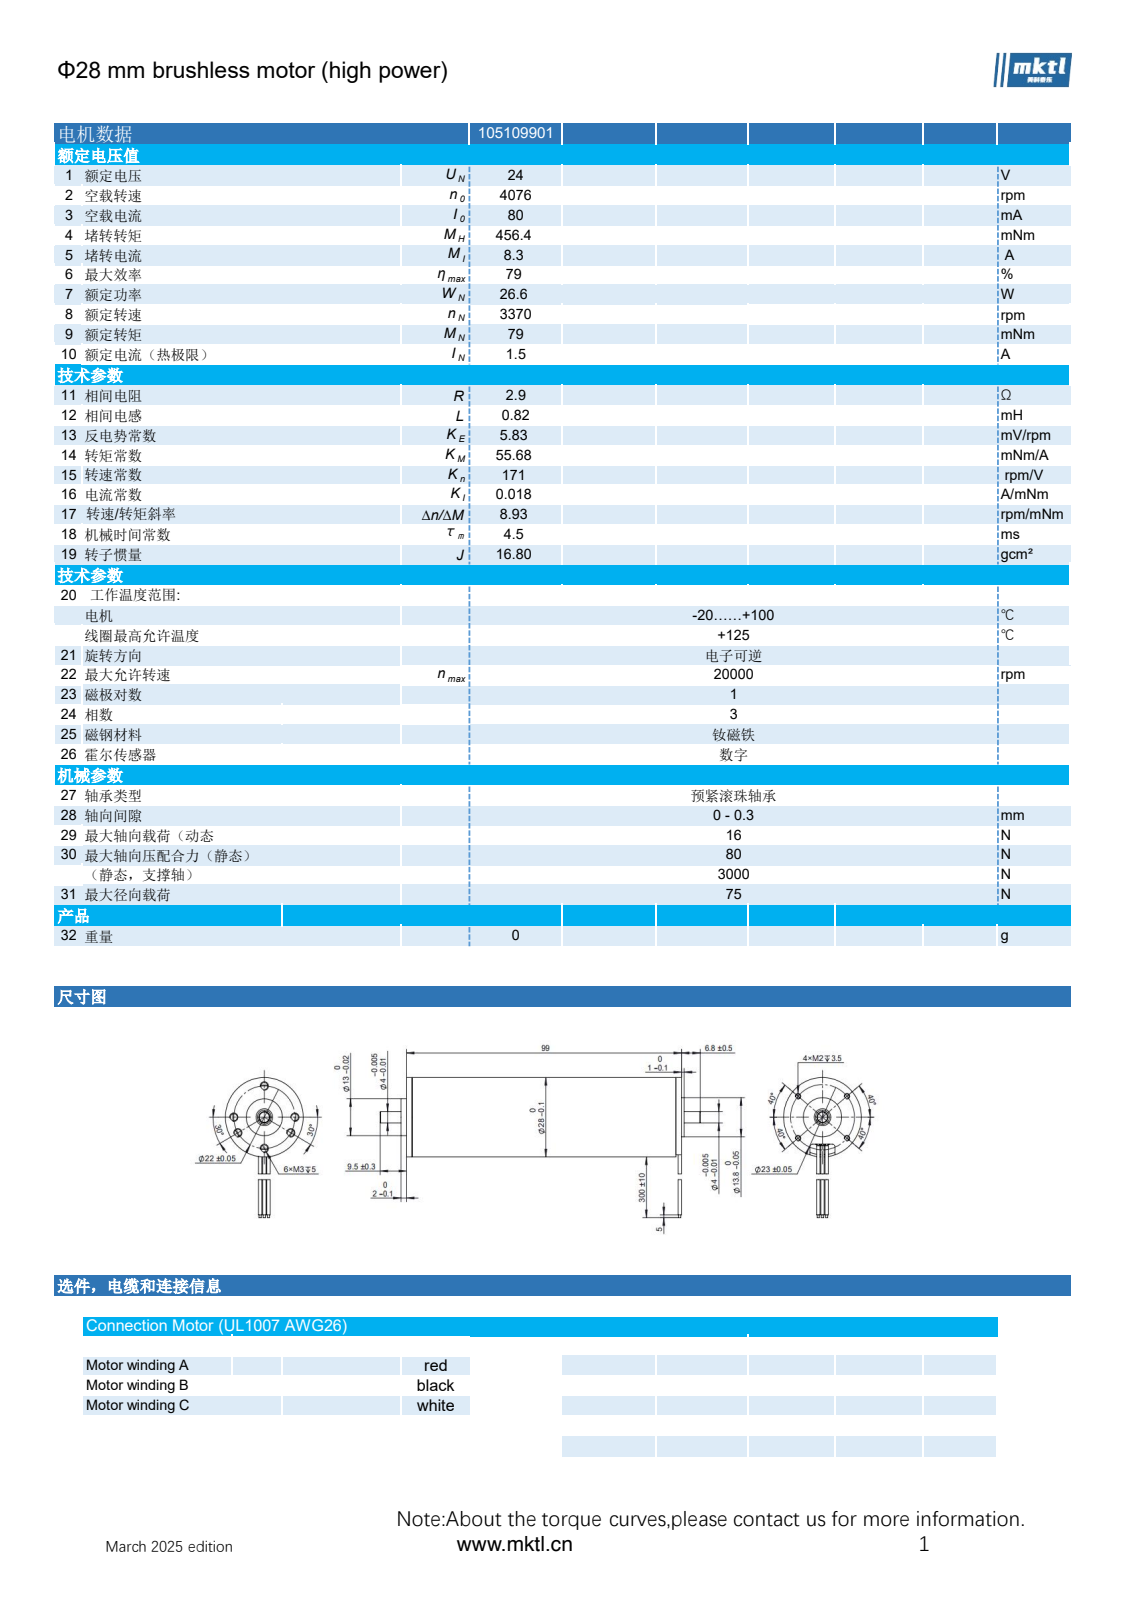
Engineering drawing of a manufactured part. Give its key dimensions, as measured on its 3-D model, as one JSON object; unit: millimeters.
{"part_name": "105109901", "step_written_by": "SolidWorks 2025 (AUTOMOTIVE_DESIGN)", "units": "millimeters", "bodies": {"solids": 430, "faces": 2708, "planar": 899, "cylindrical": 1780, "other": 29}, "overall_size": [115.3, 49.4, 28], "volume_mm3": 55030, "surface_area_mm2": 247561, "round_holes": [[2.5, 6], [1.6, 4], [4, 1], [6, 1], [8, 1], [9, 1], [14, 1], [14.5, 1], [19.5, 1], [19.7, 1], [22.7, 1]], "round_bosses_or_shafts": [[1.2, 3], [0.8, 3], [0.3, 3], [28, 1], [26.4, 1], [26.3, 1], [13.8, 1], [13, 1]], "partial_cylinders_radius": [[1, 2]], "face_to_face_distances": [0.4, 0.6, 1, 0.8, 1.2, 1.4, 1.6, 2, 1.8, 2.2], "hole_center_spacings": [11, 7.71, 9.52, 11.5, 15.56, 20.39, 21.14, 2.02]}
